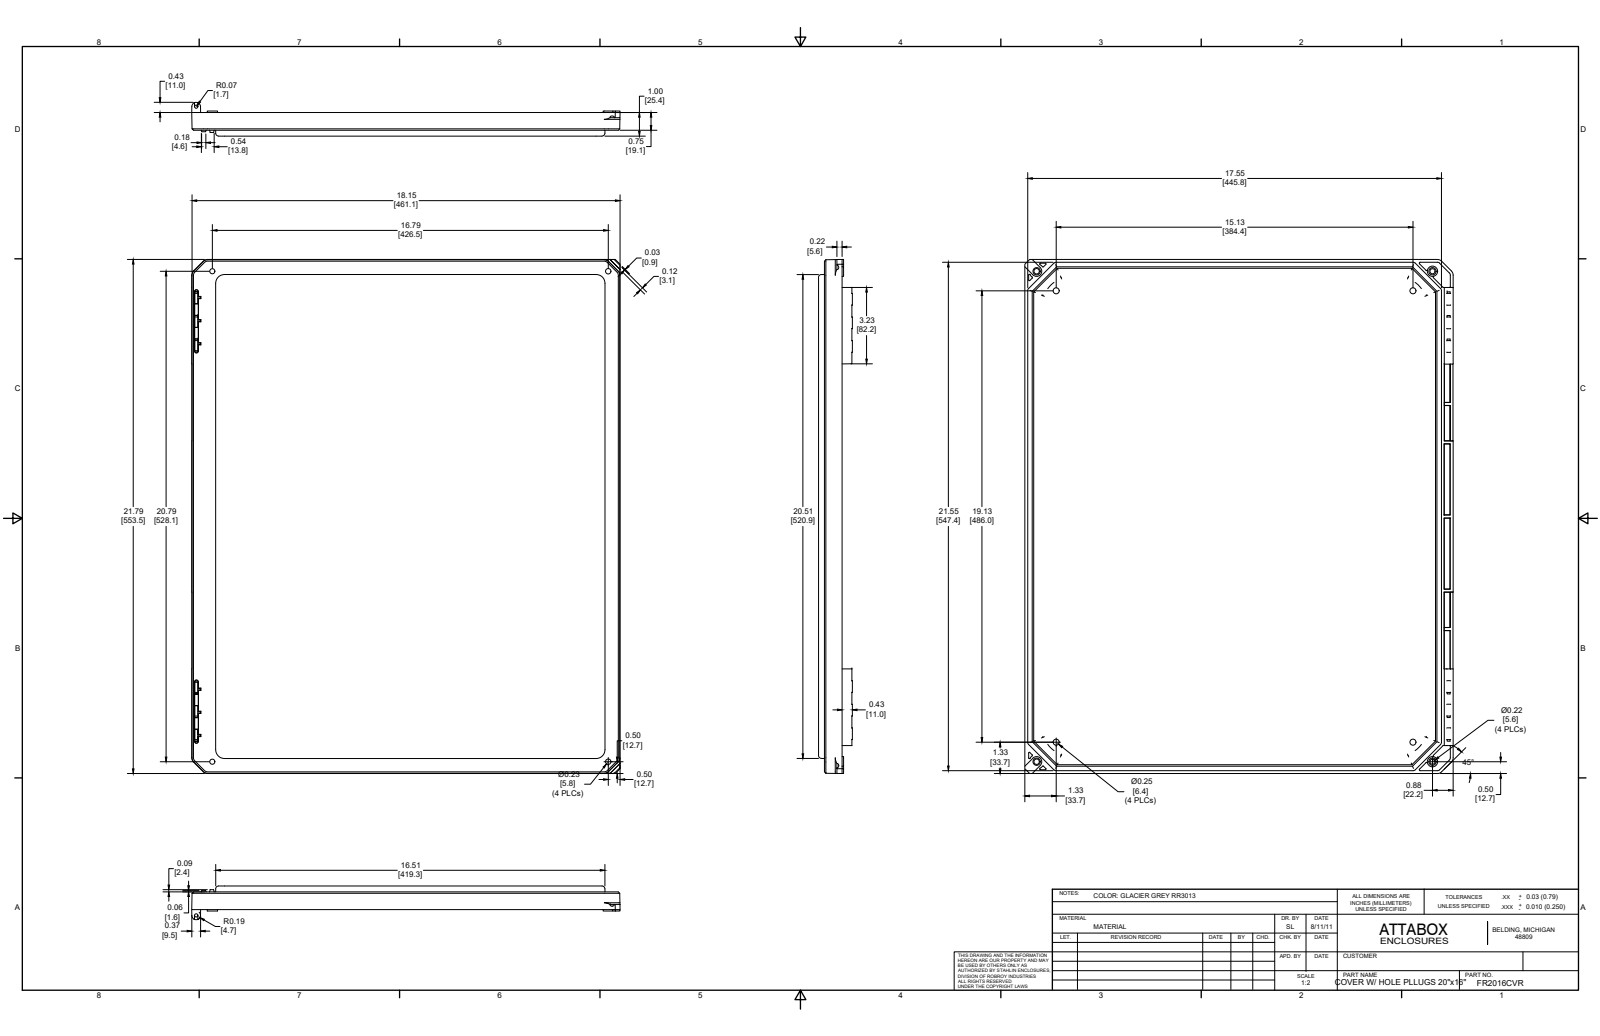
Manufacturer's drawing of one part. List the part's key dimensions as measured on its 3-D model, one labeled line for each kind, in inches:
Part name (STEP PRODUCT): FR2016CVR
STEP written by: SolidWorks 2019 (AUTOMOTIVE_DESIGN)
Units: inches
Bodies: 1 solid, 622 faces (270 planar, 200 cylindrical, 152 other)
Overall size (bounding box): 21.79 × 18.165 × 1.434
Volume: 71.73 in³ · Surface area: 974.2 in²
Round holes (diameter × count): ⌀0.253 ×4, ⌀0.219 ×2, ⌀0.227 ×2, ⌀0.313 ×2, ⌀0.137 ×1
Round bosses / shafts (diameter × count): ⌀0.435 ×2
Partial cylindrical surfaces — rounded edges, fillets, slot ends (radius × count): R0.03 ×27, R0.063 ×19, R0.01 ×18, R0.096 ×16, R0.125 ×12, R0.04 ×10, R0.06 ×9, R0.005 ×8
Main face-to-face distances: 0.125, 0.25, 0.125, 0.75, 0.375, 0.375, 1, 0.625, 0.875, 0.625
Hole centre spacings: 19.979, 1.172, 1.172, 15.133, 15.983, 15.983, 16.79, 19.133
